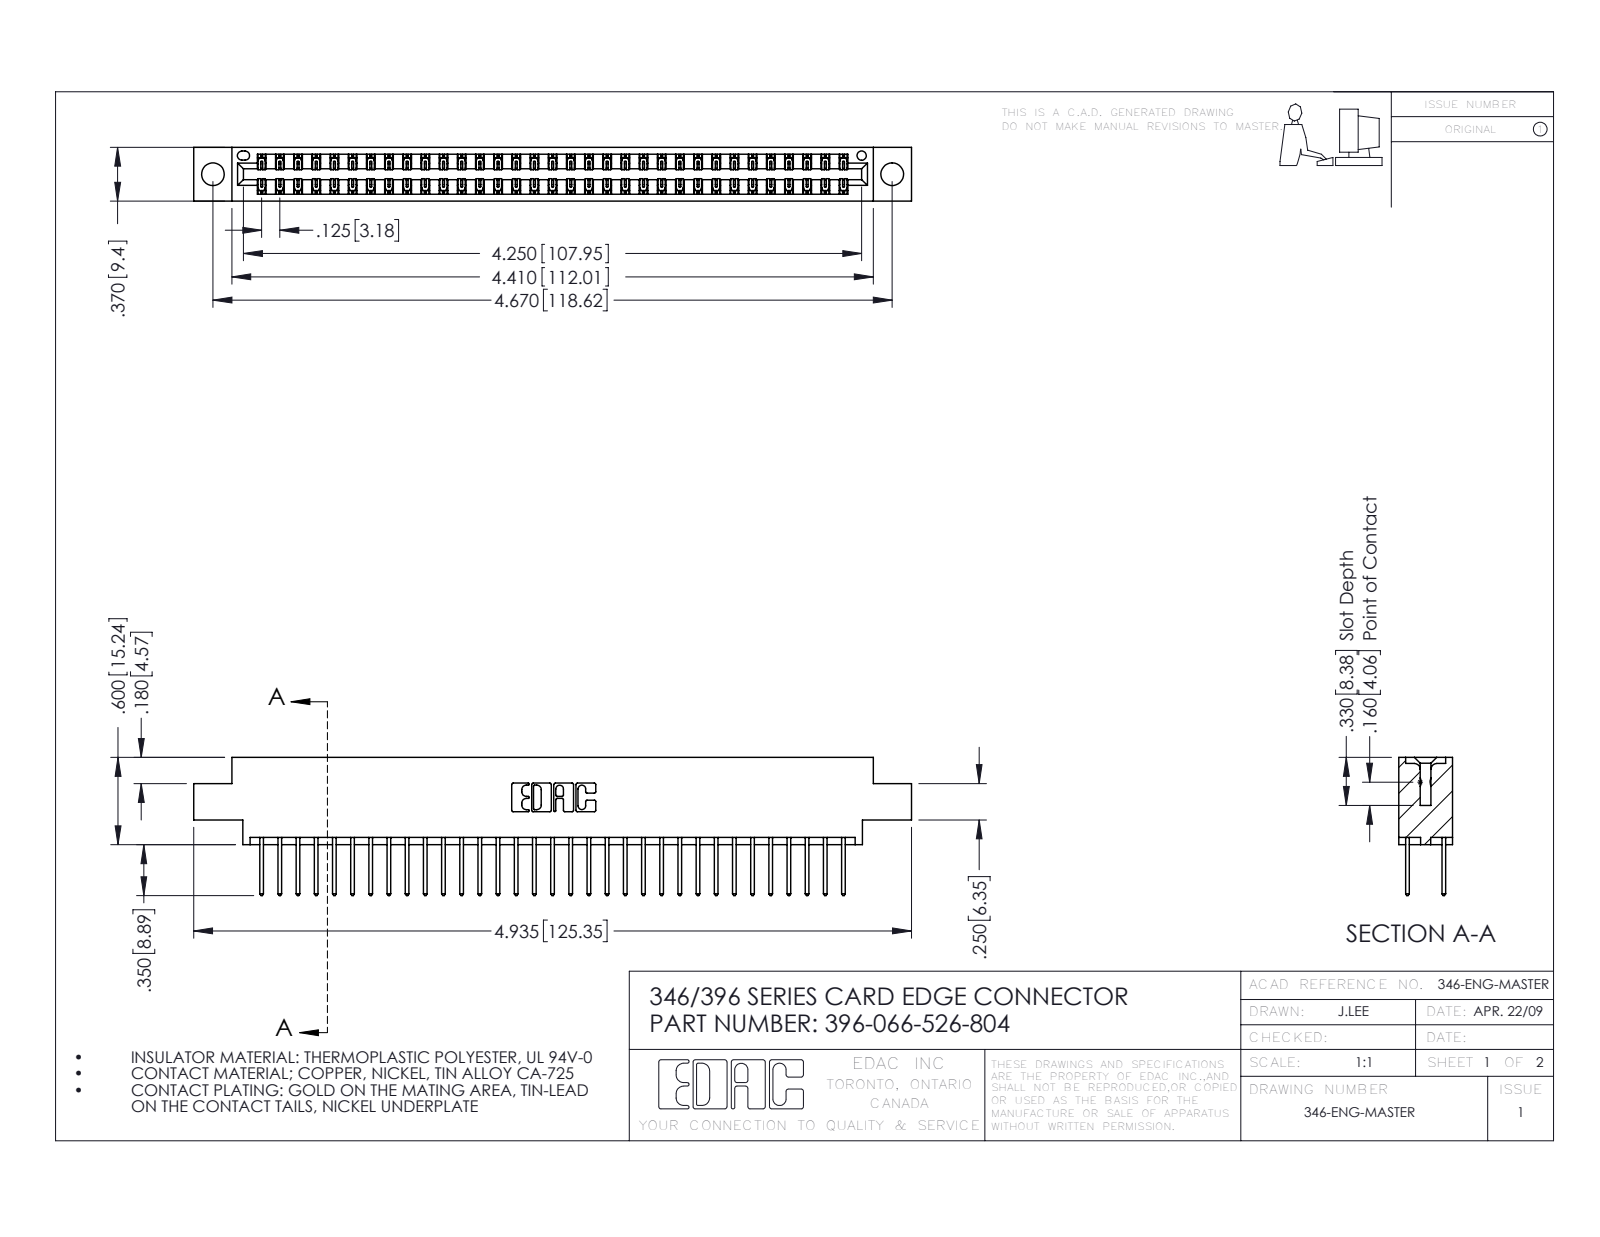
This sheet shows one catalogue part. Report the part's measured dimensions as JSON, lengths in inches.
{"part_name": "346 Part_0.170 Offset - 0.156 Dia-TH; 396-066-526-804; 345-292-001_345-293-126", "step_written_by": "SolidWorks 2016 (CONFIG_CONTROL_DESIGN)", "units": "inches", "bodies": {"solids": 67, "faces": 3558, "planar": 2390, "cylindrical": 1168, "other": 0}, "overall_size": [4.935, 0.95, 0.37], "volume_in3": 0.733, "surface_area_in2": 26.13, "round_holes": [[0.156, 2], [0.064, 1]], "partial_cylinders_radius": [[0.006, 99], [0.01, 66], [0.01, 22], [0.007, 6], [0.031, 6], [0.026, 3], [0.014, 2], [0.022, 2]], "face_to_face_distances": [0.048, 0.322, 0.25, 0.37, 0.072, 0.298, 0.025, 0.275, 0.148, 0.222], "hole_center_spacings": [0.246, 4.462, 4.67]}
